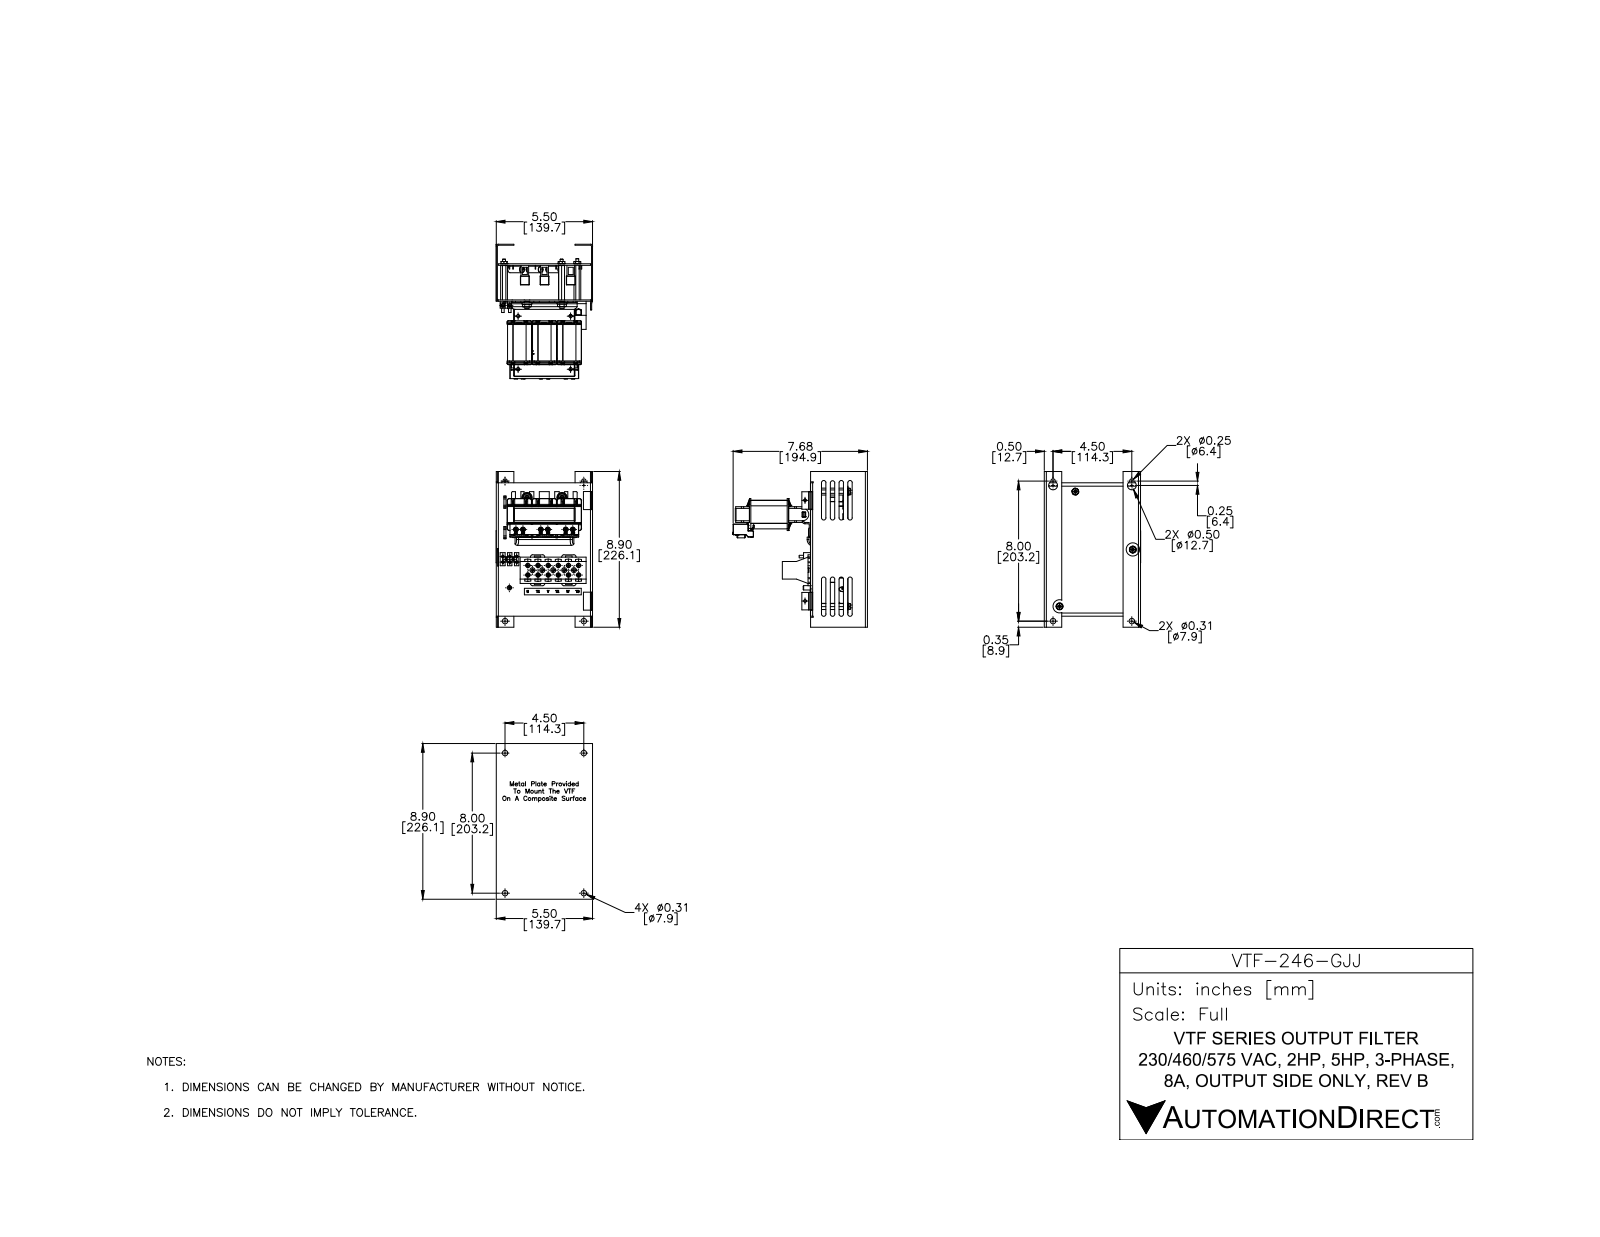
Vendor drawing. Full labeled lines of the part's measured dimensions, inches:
Part name (STEP PRODUCT): VTF 2A-12A r1 comb 1 from xt b REDUC 1 r1
STEP written by: SolidWorks 2017 (AUTOMOTIVE_DESIGN)
Units: inches
Bodies: 41 solids, 3229 faces (1936 planar, 705 cylindrical, 588 other)
Overall size (bounding box): 8.9 × 7.272 × 5.505
Volume: 22.73 in³ · Surface area: 552.6 in²
Round holes (diameter × count): ⌀0.03 ×6, ⌀0.098 ×6, ⌀0.14 ×6, ⌀0.191 ×5, ⌀0.15 ×4, ⌀0.22 ×3, ⌀0.075 ×2, ⌀0.19 ×2, ⌀0.218 ×2, ⌀0.31 ×2, ⌀0.5 ×2, ⌀0.075 ×1
Round bosses / shafts (diameter × count): ⌀0.06 ×12, ⌀0.054 ×6, ⌀0.049 ×6, ⌀0.25 ×5, ⌀0.38 ×4, ⌀0.205 ×4, ⌀0.104 ×4, ⌀0.164 ×3
Partial cylindrical surfaces — rounded edges, fillets, slot ends (radius × count): R0.03 ×48, R0.125 ×36, R0.039 ×24, R0.049 ×24, R0.07 ×12, R0.199 ×12, R0.21 ×12, R0.155 ×10
Main face-to-face distances: 0.059, 5.441, 2.063, 2, 0.063, 2.059, 2.122, 3.191, 5.382, 5.5
Hole centre spacings: 3.02, 0.789, 0.356, 1.24, 3.028, 0.214, 0.433, 0.78
